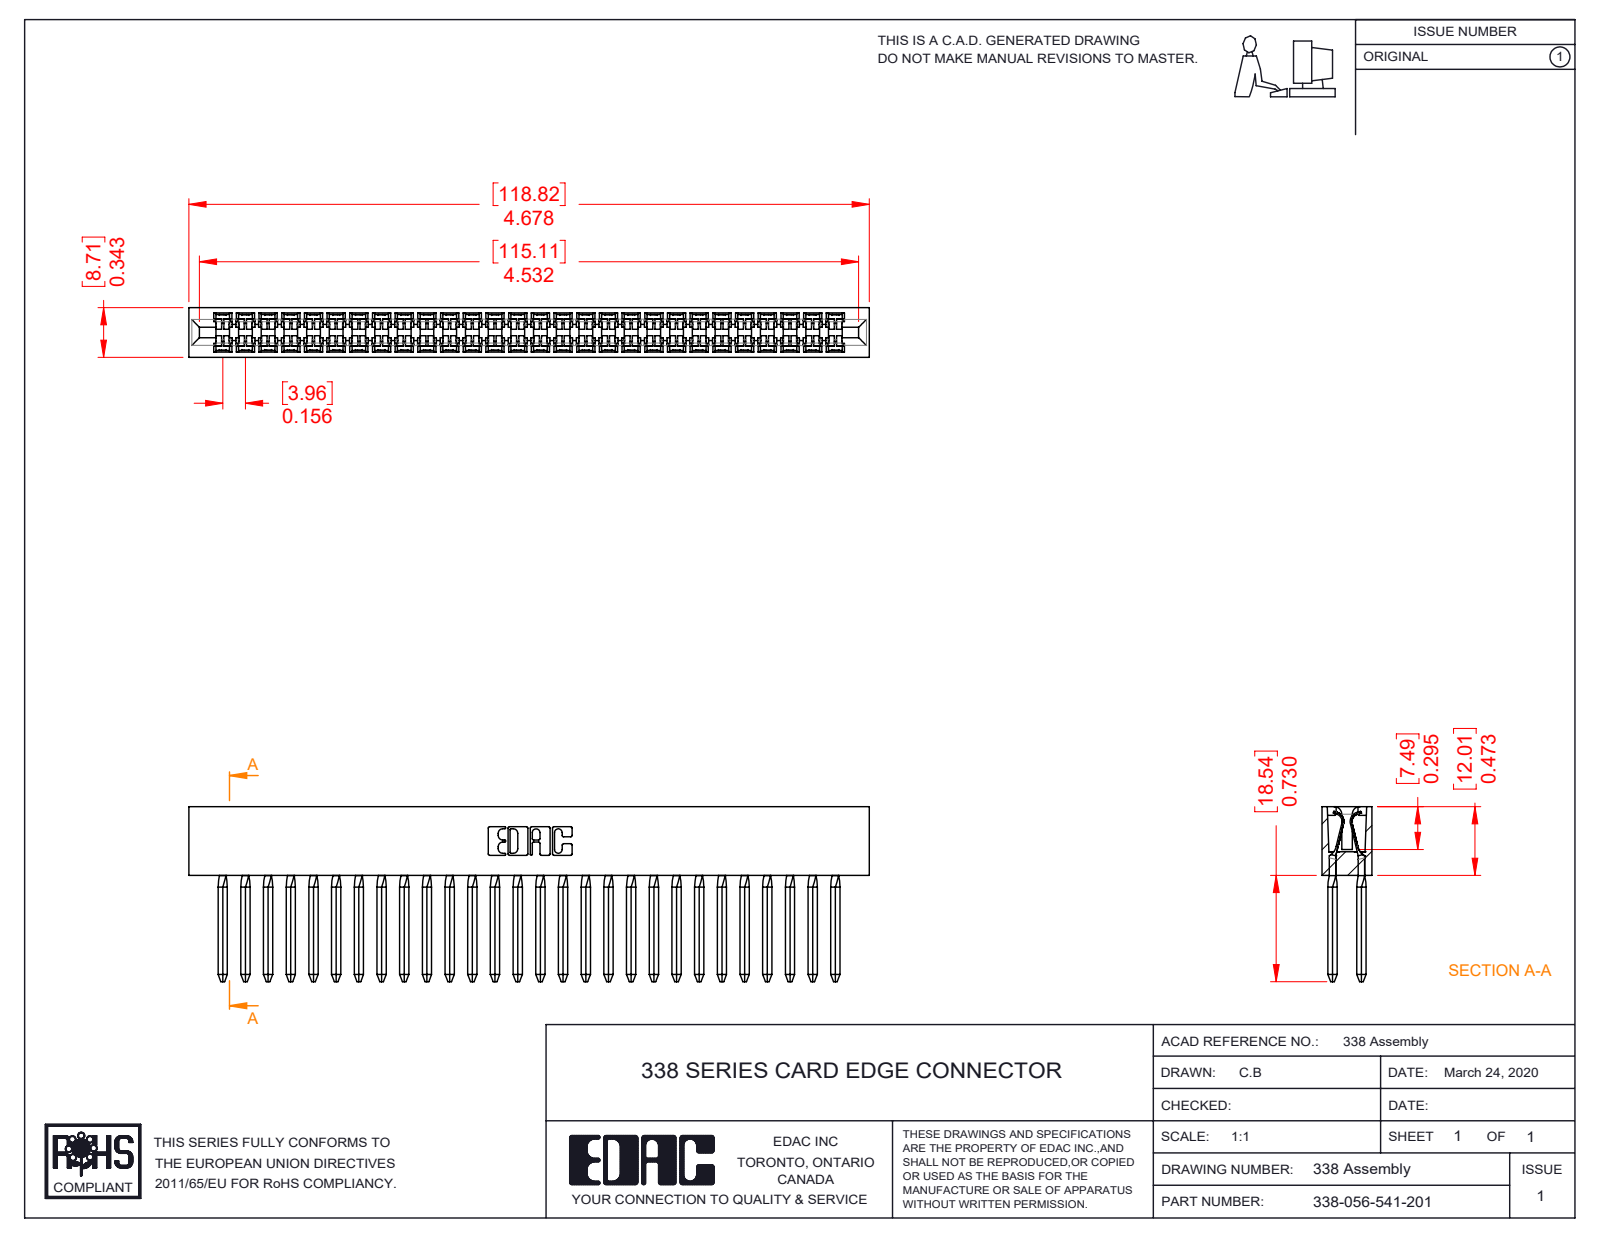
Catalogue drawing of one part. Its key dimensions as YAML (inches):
part_name: "338-210-001_338-210-028-001; 338-056-541-201; 338-290-001_541"
step_written_by: "SolidWorks 2016 (CONFIG_CONTROL_DESIGN)"
units: inches
bodies: {solids: 57, faces: 3838, planar: 2678, cylindrical: 936, other: 224}
overall_size: [4.678, 1.203, 0.343]
volume: 0.585
surface_area: 28.89
partial_cylinders:
  - {radius: 0.025, count: 170}
  - {radius: 0.008, count: 56}
  - {radius: 0.055, count: 46}
  - {radius: 0.067, count: 46}
  - {radius: 0.1, count: 44}
  - {radius: 0.01, count: 22}
  - {radius: 0.007, count: 6}
  - {radius: 0.031, count: 6}
face_to_face_distances: [0.343, 0.156, 0.624, 0.11, 0.207, 0.135, 0.78, 0.468, 0.16, 0.048]
